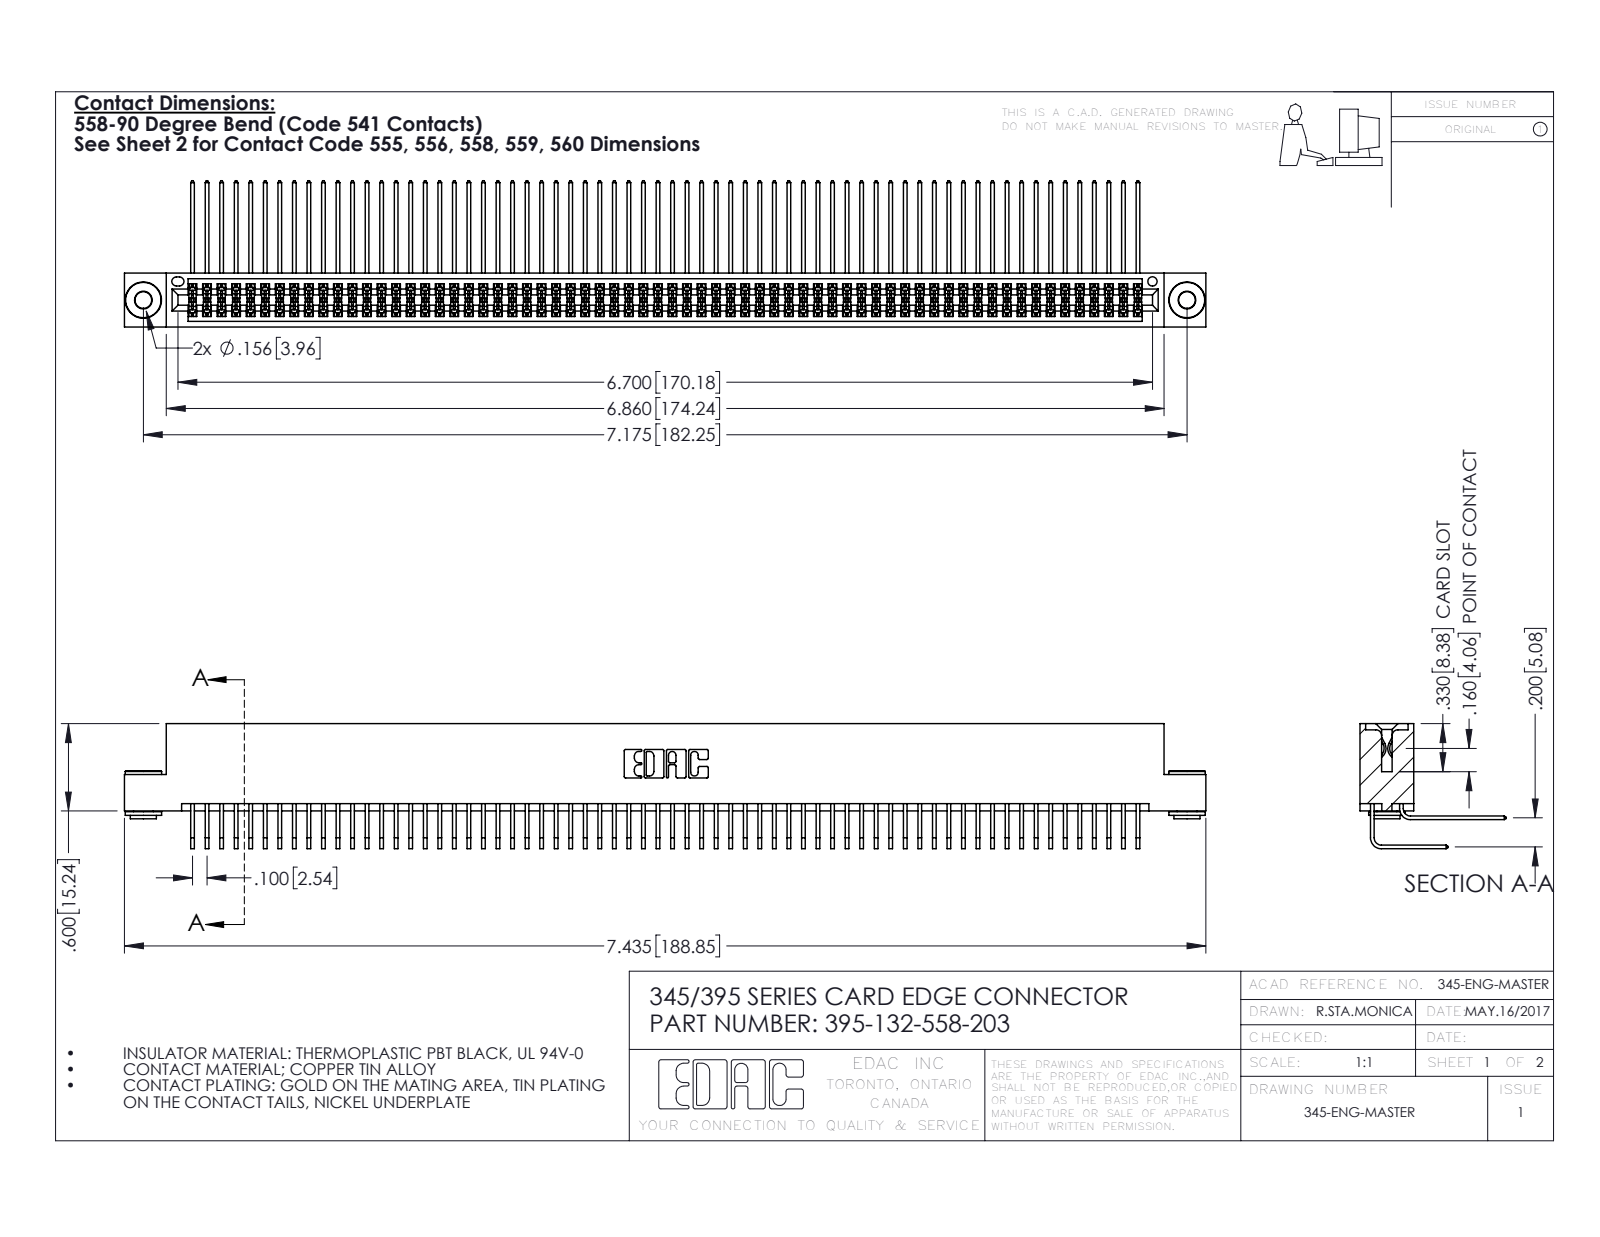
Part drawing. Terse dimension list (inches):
name: 345-292-001_558 Tail - 2; 345-292-001_558 559 Tail - 1; 345-250-002_345-250-002-102; 395-132-558-203 (+1 more)
written by: SolidWorks 2016 (CONFIG_CONTROL_DESIGN)
unit: in
bodies: 135 solids, 7028 faces (4710 planar, 2310 cylindrical, 8 other)
size: 7.435 × 1.005 × 0.859
volume: 1.181 in³; area: 50.92 in²
holes: 2× ⌀0.116, 2× ⌀0.156, 1× ⌀0.064
bosses: 2× ⌀0.25, 2× ⌀0.18, 2× ⌀0.136
rounds: 199× R0.006, 22× R0.01, 6× R0.007, 6× R0.031, 3× R0.026, 2× R0.014, 2× R0.019, 2× R0.022
face distances: 0.072, 0.298, 0.2, 0.37, 0.025, 0.098, 0.272, 0.225, 0.025, 0.175
hole spacings: 0.27, 6.939, 7.175
